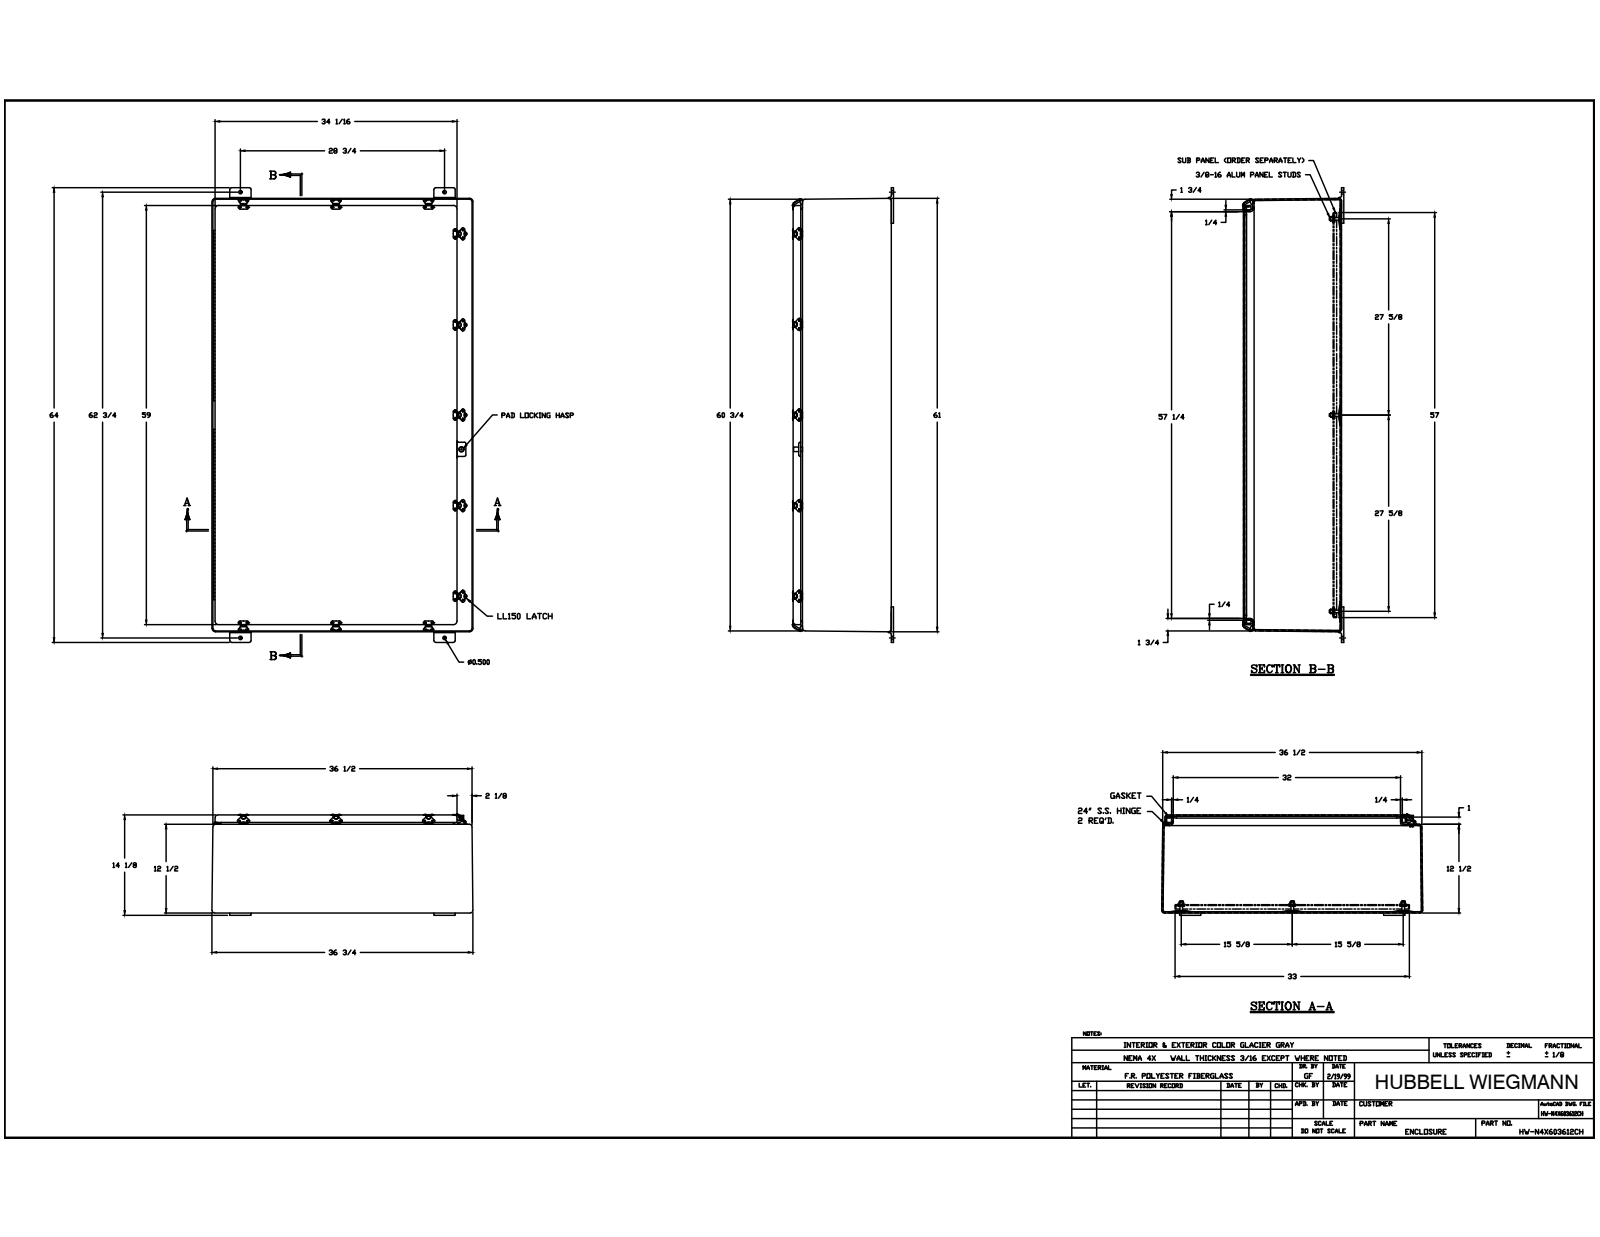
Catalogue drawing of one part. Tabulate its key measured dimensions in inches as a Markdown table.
| quantity | value |
| --- | --- |
| part name | WPN603612SHWT; WPN603612HWTPCVR; N603612G; WP3036HWU (+8 more) |
| STEP written by | Autodesk Inventor 2014 (AUTOMOTIVE_DESIGN) |
| units | inches |
| bodies | 127 solids, 3132 faces (1212 planar, 1300 cylindrical, 620 other) |
| overall size | 64 × 36.75 × 14.366 |
| volume | 1 308 in³ |
| surface area | 15 480 in² |
| round holes (diameter × count) | 0.13 × 72, 0.063 × 44, 0.138 × 22, 0.187 × 22, 0.065 × 16, 0.375 × 8, 0.5 × 4, 0.135 × 3, 0.156 × 3, 0.125 × 1, 0.201 × 1, 0.25 × 1 |
| round bosses / shafts (diameter × count) | 0.14 × 44, 0.297 × 16, 0.5 × 11, 0.2 × 3, 0.25 × 1, 0.201 × 1 |
| partial cylindrical surfaces (radius × count) | 0.01 × 243, 0.03 × 44, 0.313 × 41, 0.375 × 23, 0.21 × 22, 1.186 × 22, 0.25 × 18, 0.037 × 14 |
| main face-to-face distances | 0.187, 0.125, 0.188, 13.813, 13.687, 13.624, 13.499, 36.562, 60.813, 36.75 |
| hole center spacings | 7.5, 15.5, 28, 12.75, 1, 8, 12.5, 13.031 |
